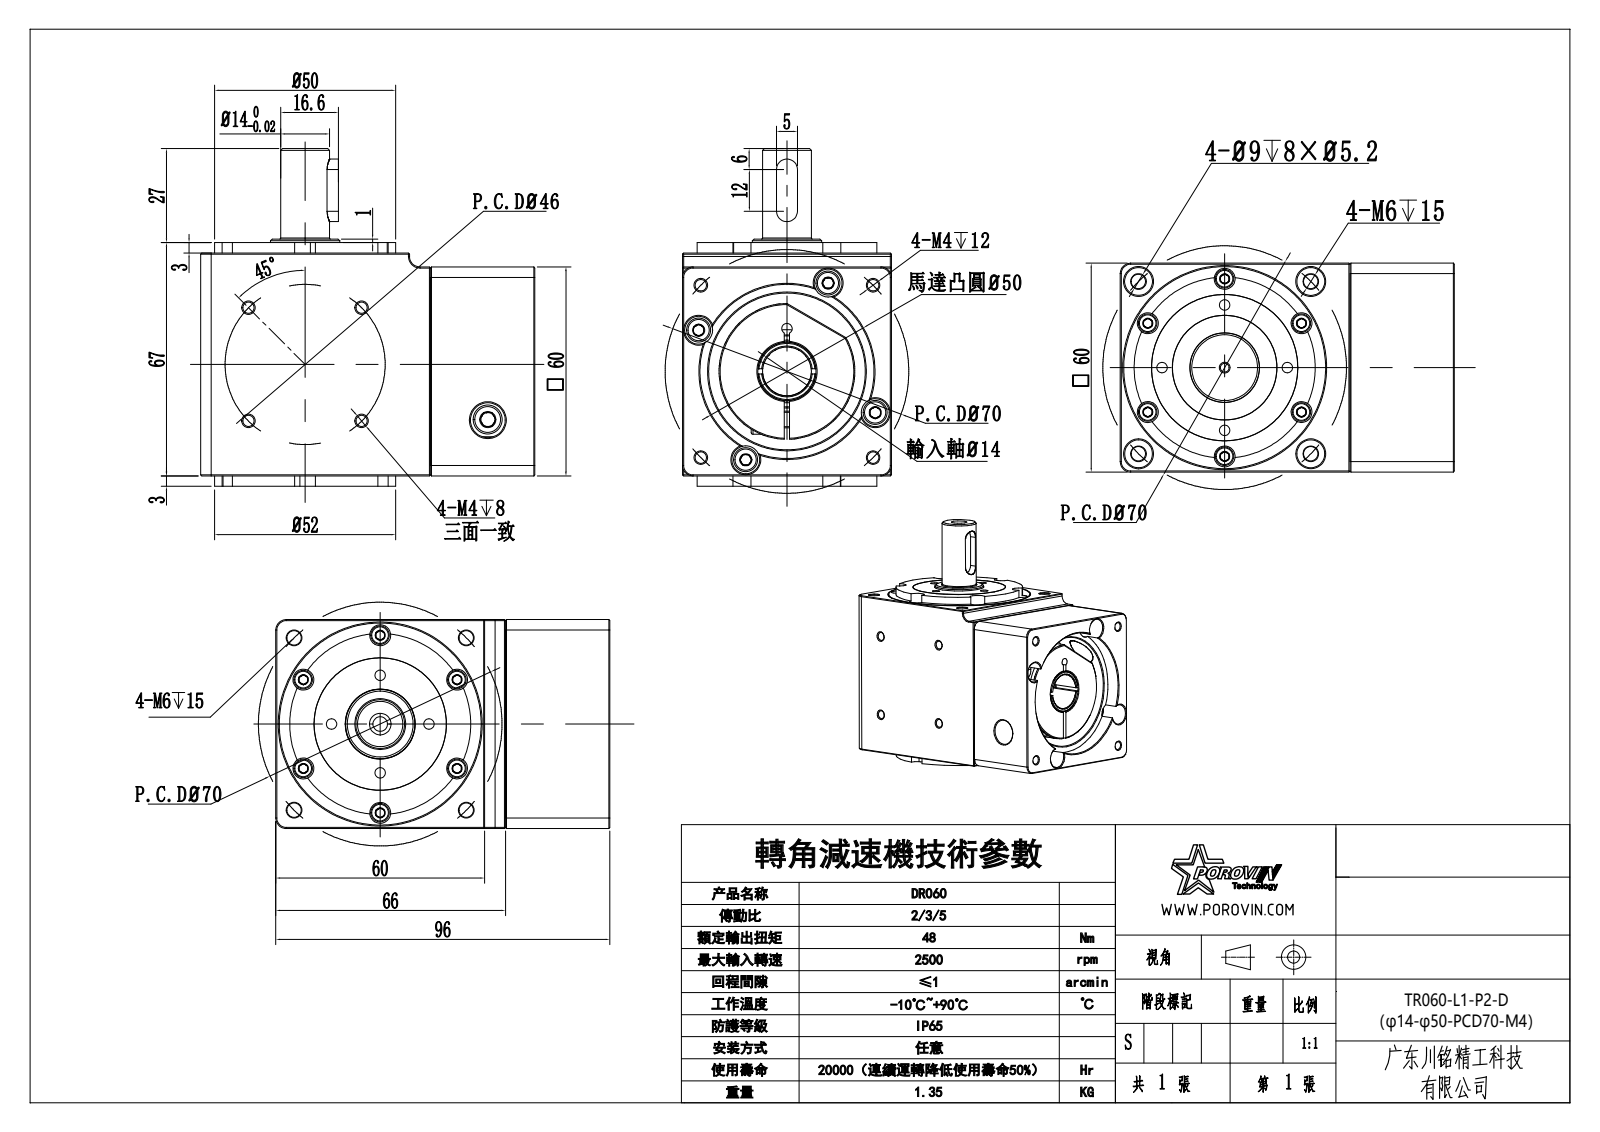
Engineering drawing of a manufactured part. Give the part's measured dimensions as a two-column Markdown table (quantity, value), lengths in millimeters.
| quantity | value |
| --- | --- |
| part name | DR060-02_03-05_-14-30-50-70-M4 |
| STEP written by | CREO PARAMETRIC BY PTC INC, 2018070 (CONFIG_CONTROL_DESIGN) |
| units | millimeters |
| bodies | 1 solid, 1033 faces (374 planar, 277 cylindrical, 382 other) |
| overall size | 97.01 × 96 × 60 |
| volume | 331 101 mm³ |
| surface area | 58 225 mm² |
| round holes (diameter × count) | 3.3 × 16, 3 × 9, 3.5 × 6, 6 × 6, 4.5 × 4, 5.1 × 4, 8 × 4, 9 × 4, 4.2 × 2, 10 × 2, 2.5 × 1, 5.5 × 1 |
| round bosses / shafts (diameter × count) | 5.5 × 6, 2.87 × 6, 7 × 4, 3.84 × 4, 58 × 1, 39 × 1, 30 × 1, 19.9 × 1 |
| partial cylindrical surfaces (radius × count) | 3 × 7, 2.5 × 2, 5.5 × 1, 25 × 1, 26 × 1, 27.45 × 1 |
| main face-to-face distances | 60, 3, 67, 4, 7, 63, 70, 64, 96, 24 |
| hole center spacings | 25.5, 22.8, 25.65, 26.98, 32.52, 35, 45.98, 49.4 |
